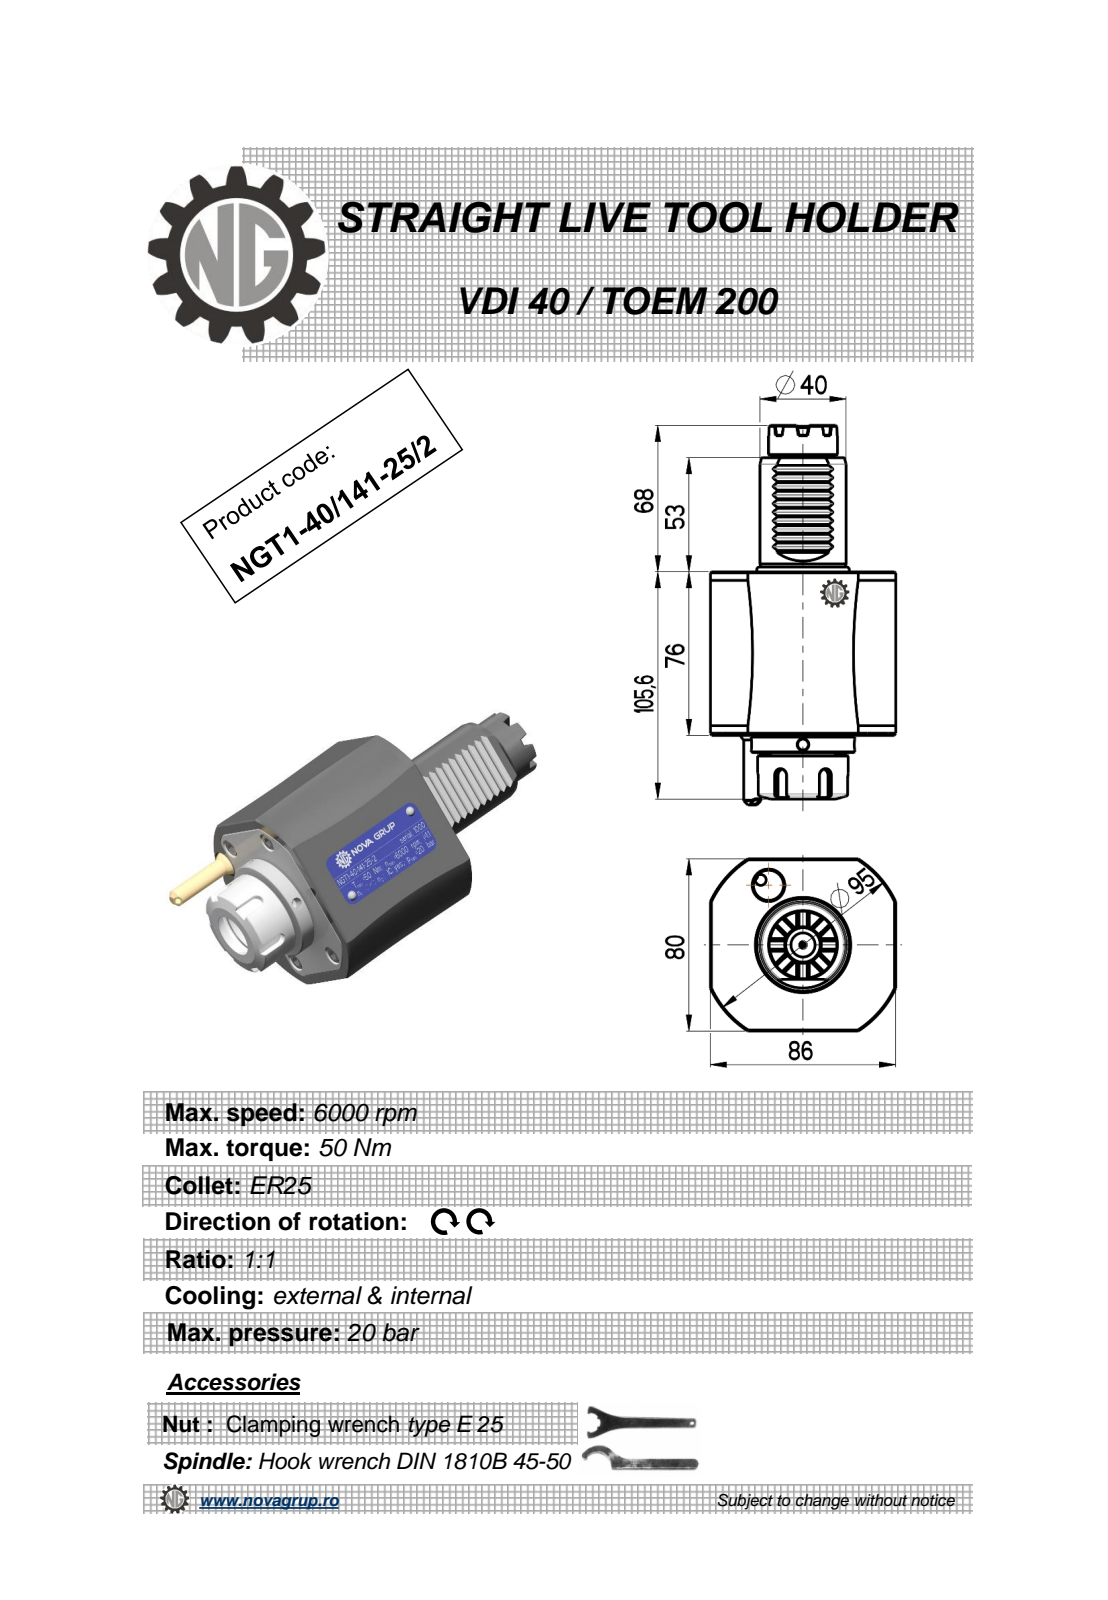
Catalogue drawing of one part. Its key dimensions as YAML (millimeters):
part_name: "NGT1_40_141_25_1"
step_written_by: "PRO/ENGINEER BY PARAMETRIC TECHNOLOGY CORPORATION, 2010280 (CONFIG_CONTROL_DESIGN)"
units: millimeters
bodies: {solids: 1, faces: 346, planar: 141, cylindrical: 60, other: 145}
overall_size: [176.34, 86, 81.6]
volume: 588490
surface_area: 52316
round_holes:
  - {diameter: 5, count: 3}
  - {diameter: 3, count: 1}
  - {diameter: 20.3, count: 1}
round_bosses_or_shafts:
  - {diameter: 48, count: 1}
  - {diameter: 42, count: 1}
  - {diameter: 41.5, count: 1}
  - {diameter: 40, count: 1}
  - {diameter: 33, count: 1}
  - {diameter: 32, count: 1}
  - {diameter: 17.2, count: 1}
  - {diameter: 8, count: 1}
partial_cylinders:
  - {radius: 0.3, count: 10}
  - {radius: 0.22, count: 6}
  - {radius: 3, count: 5}
  - {radius: 47.5, count: 1}
face_to_face_distances: [76, 80, 86, 84, 8, 2.83, 5.66, 53, 129, 137]
hole_center_spacings: [40]
